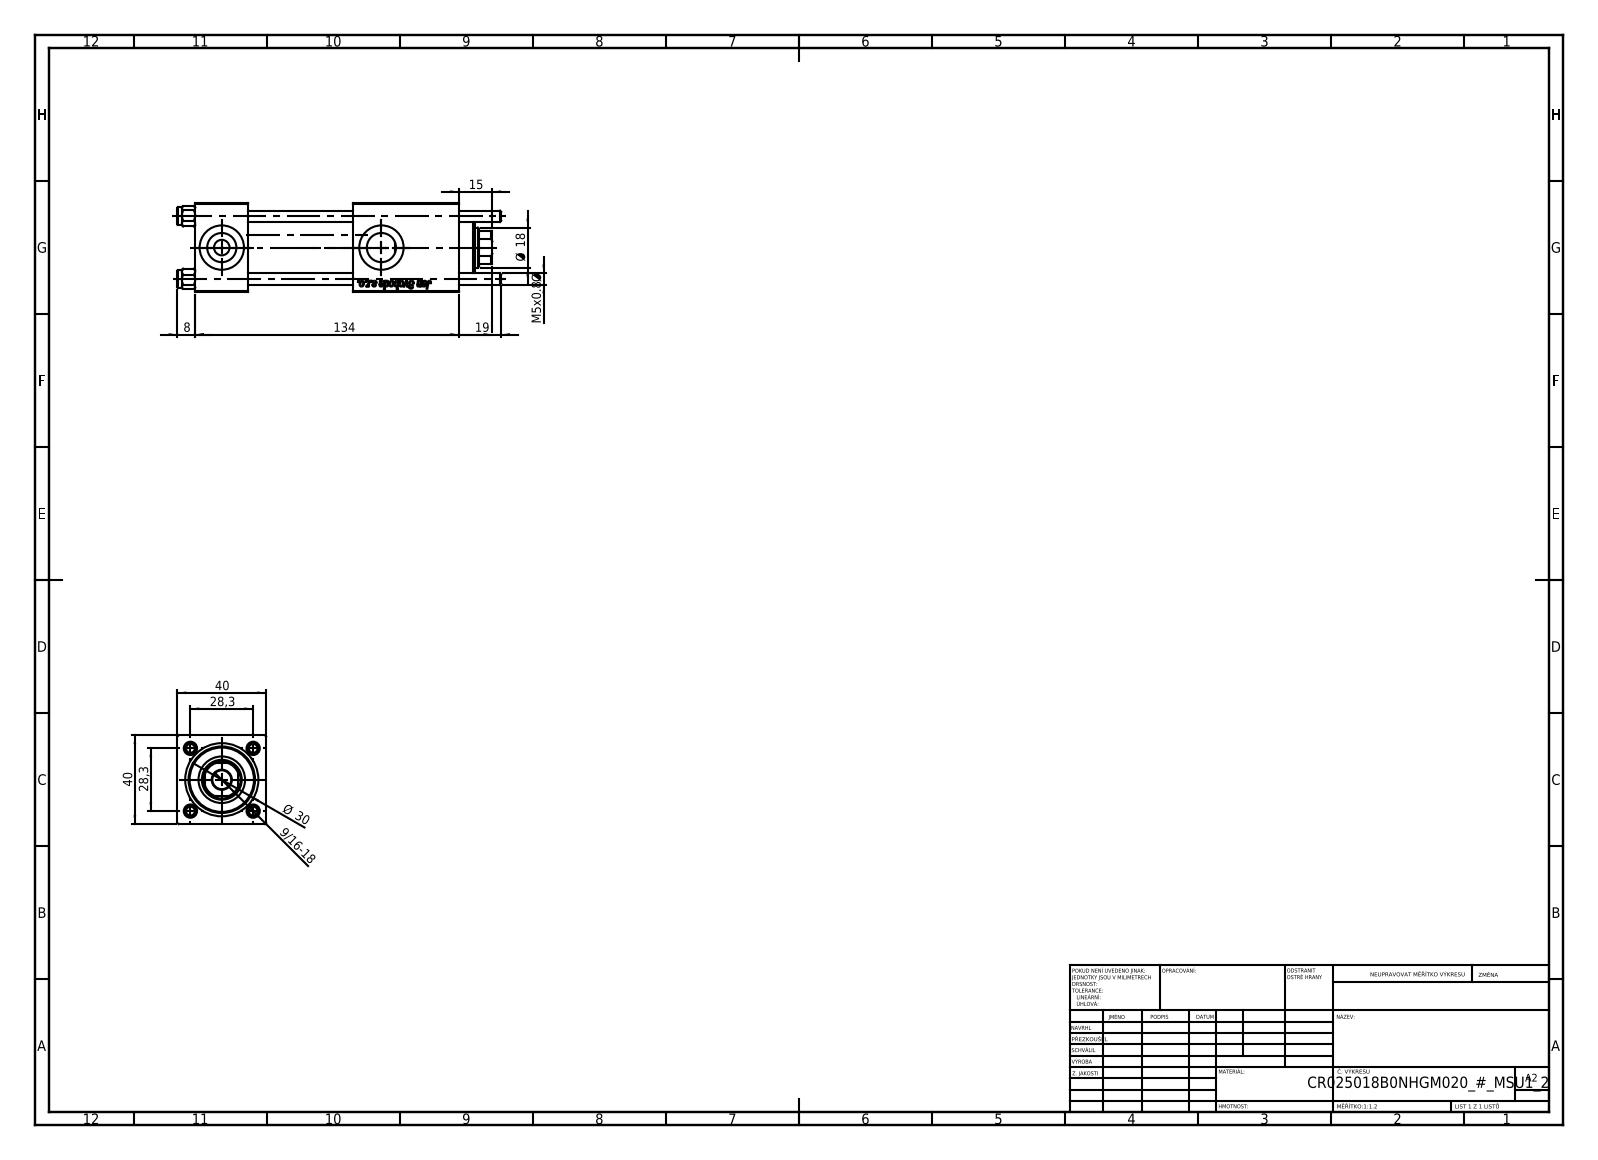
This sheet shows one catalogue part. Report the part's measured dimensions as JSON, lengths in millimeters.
{"part_name": "V215CR_VCP_B; V215CR_B_TYCINKA; NUT_M5_B; V215CR_B-1 (+1 more)", "step_written_by": "SolidWorks 2019 (CONFIG_CONTROL_DESIGN)", "units": "millimeters", "bodies": {"solids": 11, "faces": 1152, "planar": 428, "cylindrical": 76, "other": 648}, "overall_size": [146, 40, 40], "volume_mm3": 152491, "surface_area_mm2": 60895, "round_holes": [[5, 4], [20, 3], [7, 2], [13.16, 2], [8.5, 1], [18, 1], [21, 1], [25, 1], [30, 1]], "round_bosses_or_shafts": [[8, 4], [31, 1]], "partial_cylinders_radius": [[8.5, 1]], "face_to_face_distances": [40, 24, 71, 47, 90.3, 66.3, 19.3, 119, 95, 48], "hole_center_spacings": [20.01, 28.3, 40.02, 72]}
